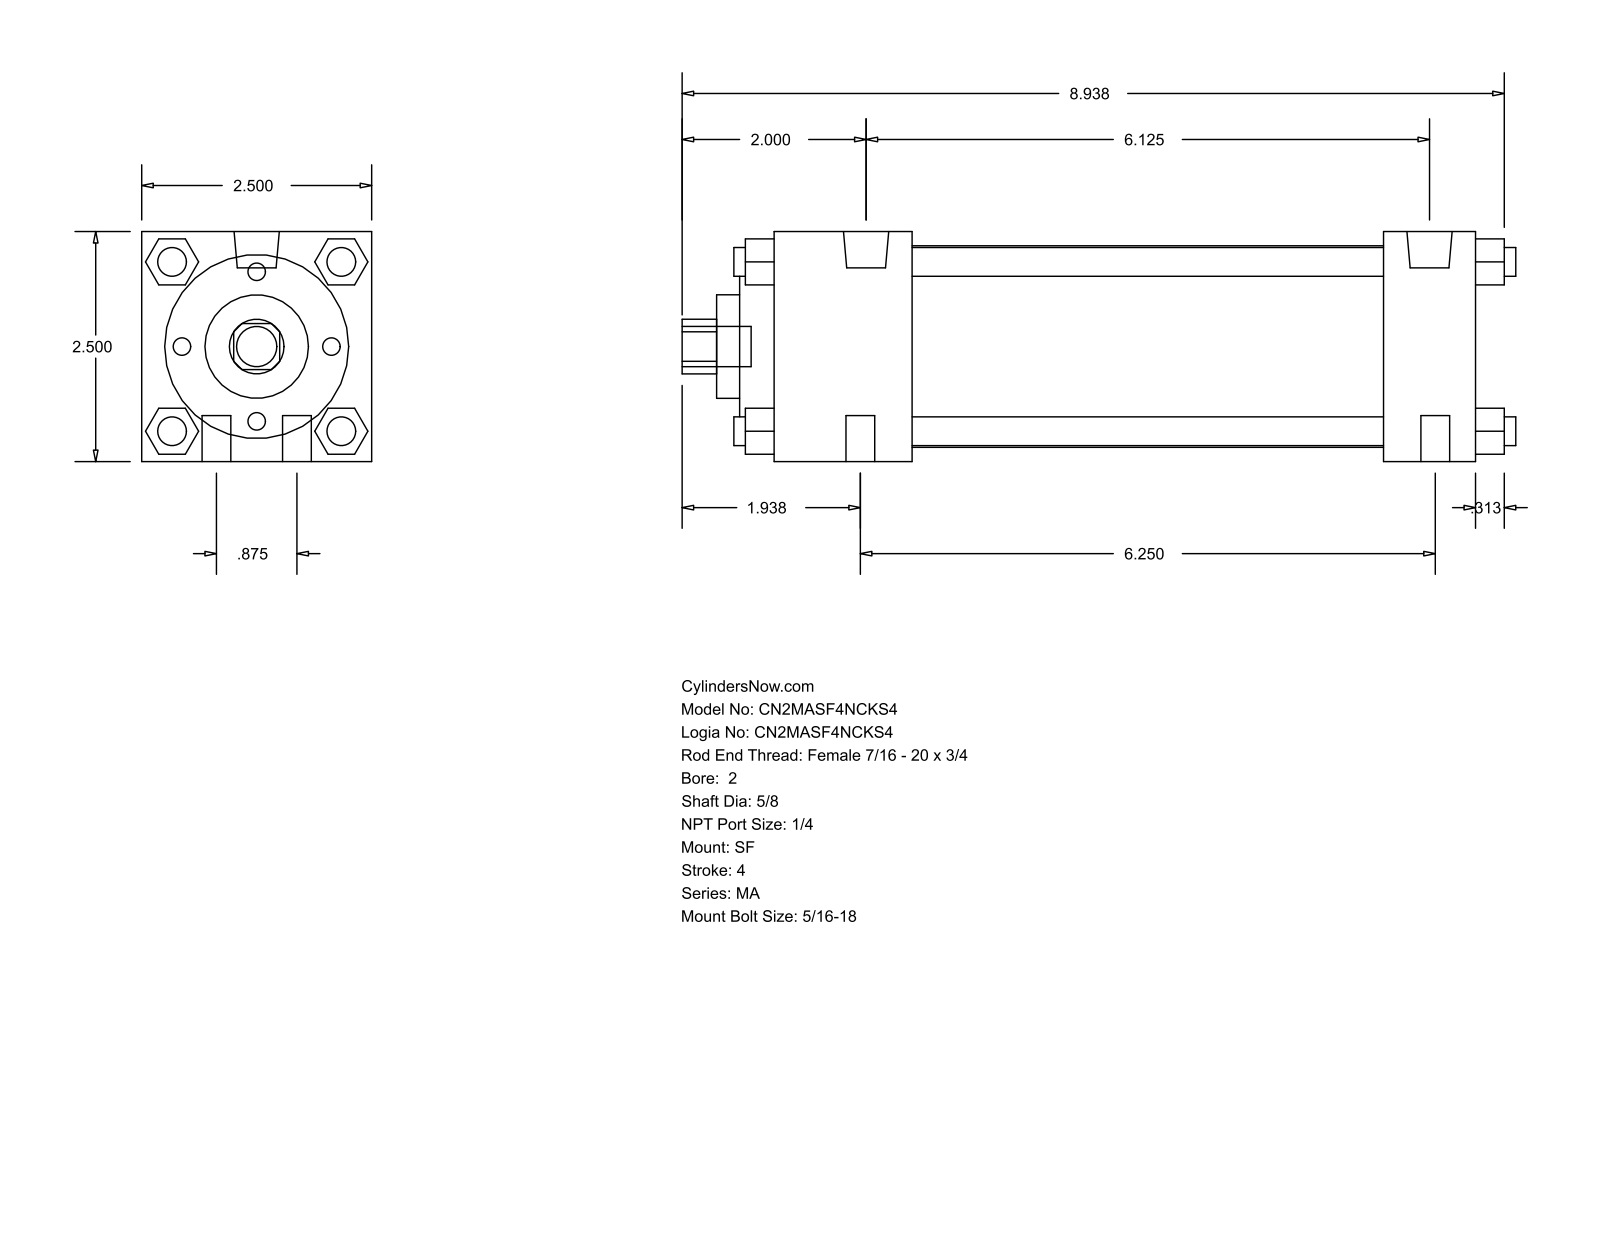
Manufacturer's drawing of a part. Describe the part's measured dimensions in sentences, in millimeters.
The part is named "MA_SF__0200_0.625". Its 3-D file was written by "GSSL Pune (CONFIG_CONTROL_DESIGN)". It is 0 solids with 126 faces: 95 planar, 31 cylindrical and 0 other. Overall it measures 230.19 by 63.5 by 63.5 millimeters. Round holes: 1 of diameter 15.88, 1 of diameter 28.57, 1 of diameter 50.8, 1 of diameter 55.63. Round bosses or shafts: 10 of diameter 7.94, 2 of diameter 12.49, 1 of diameter 11.11. Partial cylindrical surfaces (rounded edges, fillets, slot ends): 1 of radius 7.54. The main face-to-face distances are 63.5, 12.7, 38.1, 9.52, 193.67, 168.28, 25.39, 130.18, 155.57, 47.62.
